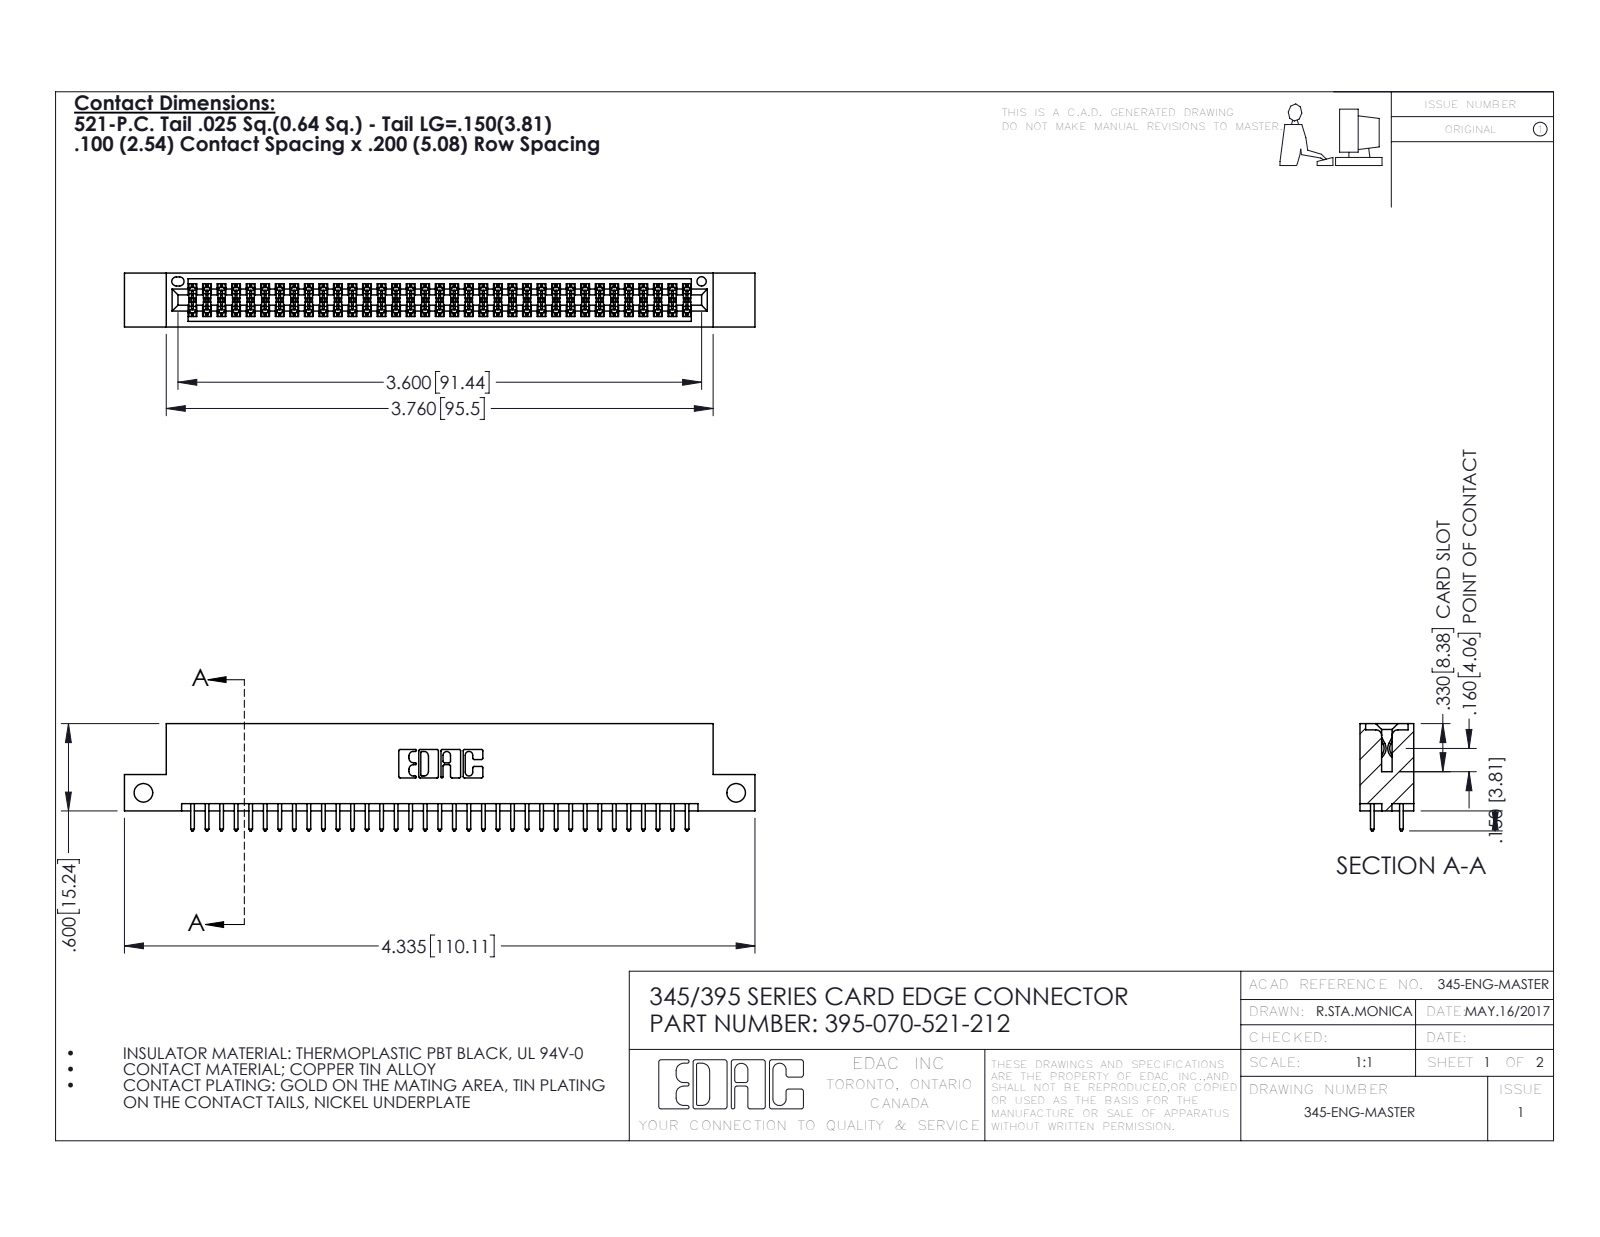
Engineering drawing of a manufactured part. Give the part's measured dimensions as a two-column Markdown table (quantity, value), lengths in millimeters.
| quantity | value |
| --- | --- |
| part name | 345 Part_Flush Mounting Lugs - Side Mount; 345-292-001_345-293-121; 395-070-521-212 |
| STEP written by | SolidWorks 2016 (CONFIG_CONTROL_DESIGN) |
| units | millimeters |
| bodies | 71 solids, 3626 faces (2390 planar, 1236 cylindrical, 0 other) |
| overall size | 110.1 × 18.7 × 9.4 |
| volume | 10 500 mm³ |
| surface area | 15 080 mm² |
| round holes (diameter × count) | 3.3 × 2, 1.6 × 1 |
| partial cylindrical surfaces (radius × count) | 0.2 × 105, 0.3 × 70, 0.3 × 22, 0.2 × 6, 0.8 × 6, 0.7 × 3, 0.4 × 2, 0.5 × 2 |
| main face-to-face distances | 7.6, 1.8, 5.1, 9.4, 2.5, 6.9, 0.6, 5.7, 4.4, 3.8 |
| hole center spacings | 103.5 |
